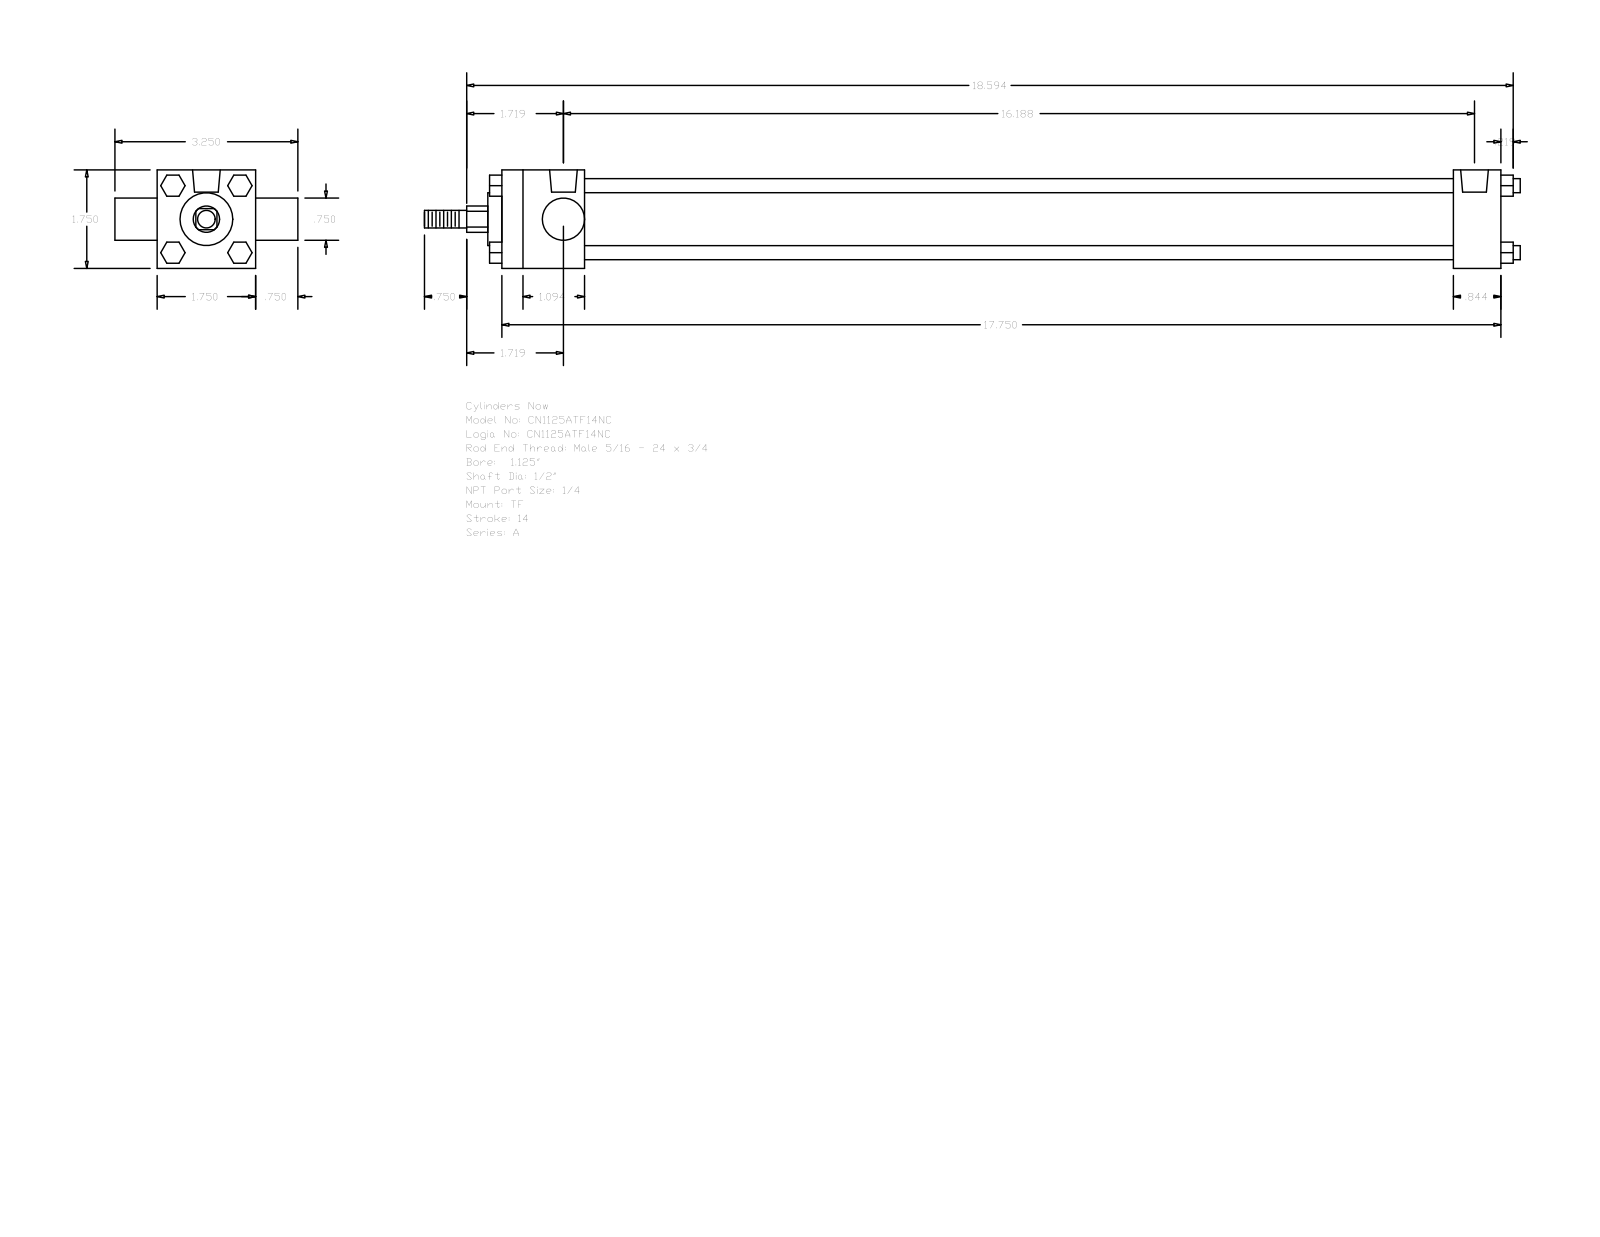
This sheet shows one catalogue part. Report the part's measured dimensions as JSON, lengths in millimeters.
{"part_name": "A_TF__0112_0.5", "step_written_by": "GSSL Pune (CONFIG_CONTROL_DESIGN)", "units": "millimeters", "bodies": {"solids": 0, "faces": 120, "planar": 92, "cylindrical": 28, "other": 0}, "overall_size": [494.51, 82.55, 44.45], "round_holes": [[5.56, 3], [12.49, 2]], "round_bosses_or_shafts": [[6.35, 4], [31.88, 1], [23.81, 1], [19.05, 1], [12.7, 1], [7.94, 1]], "partial_cylinders_radius": [[5.94, 1]], "face_to_face_distances": [44.46, 450.85, 429.41, 21.44, 37.3, 392.11, 413.55, 19.04, 63.5, 9.53], "hole_center_spacings": [1.58, 1.59, 407.99, 409.57, 409.58, 411.16]}
